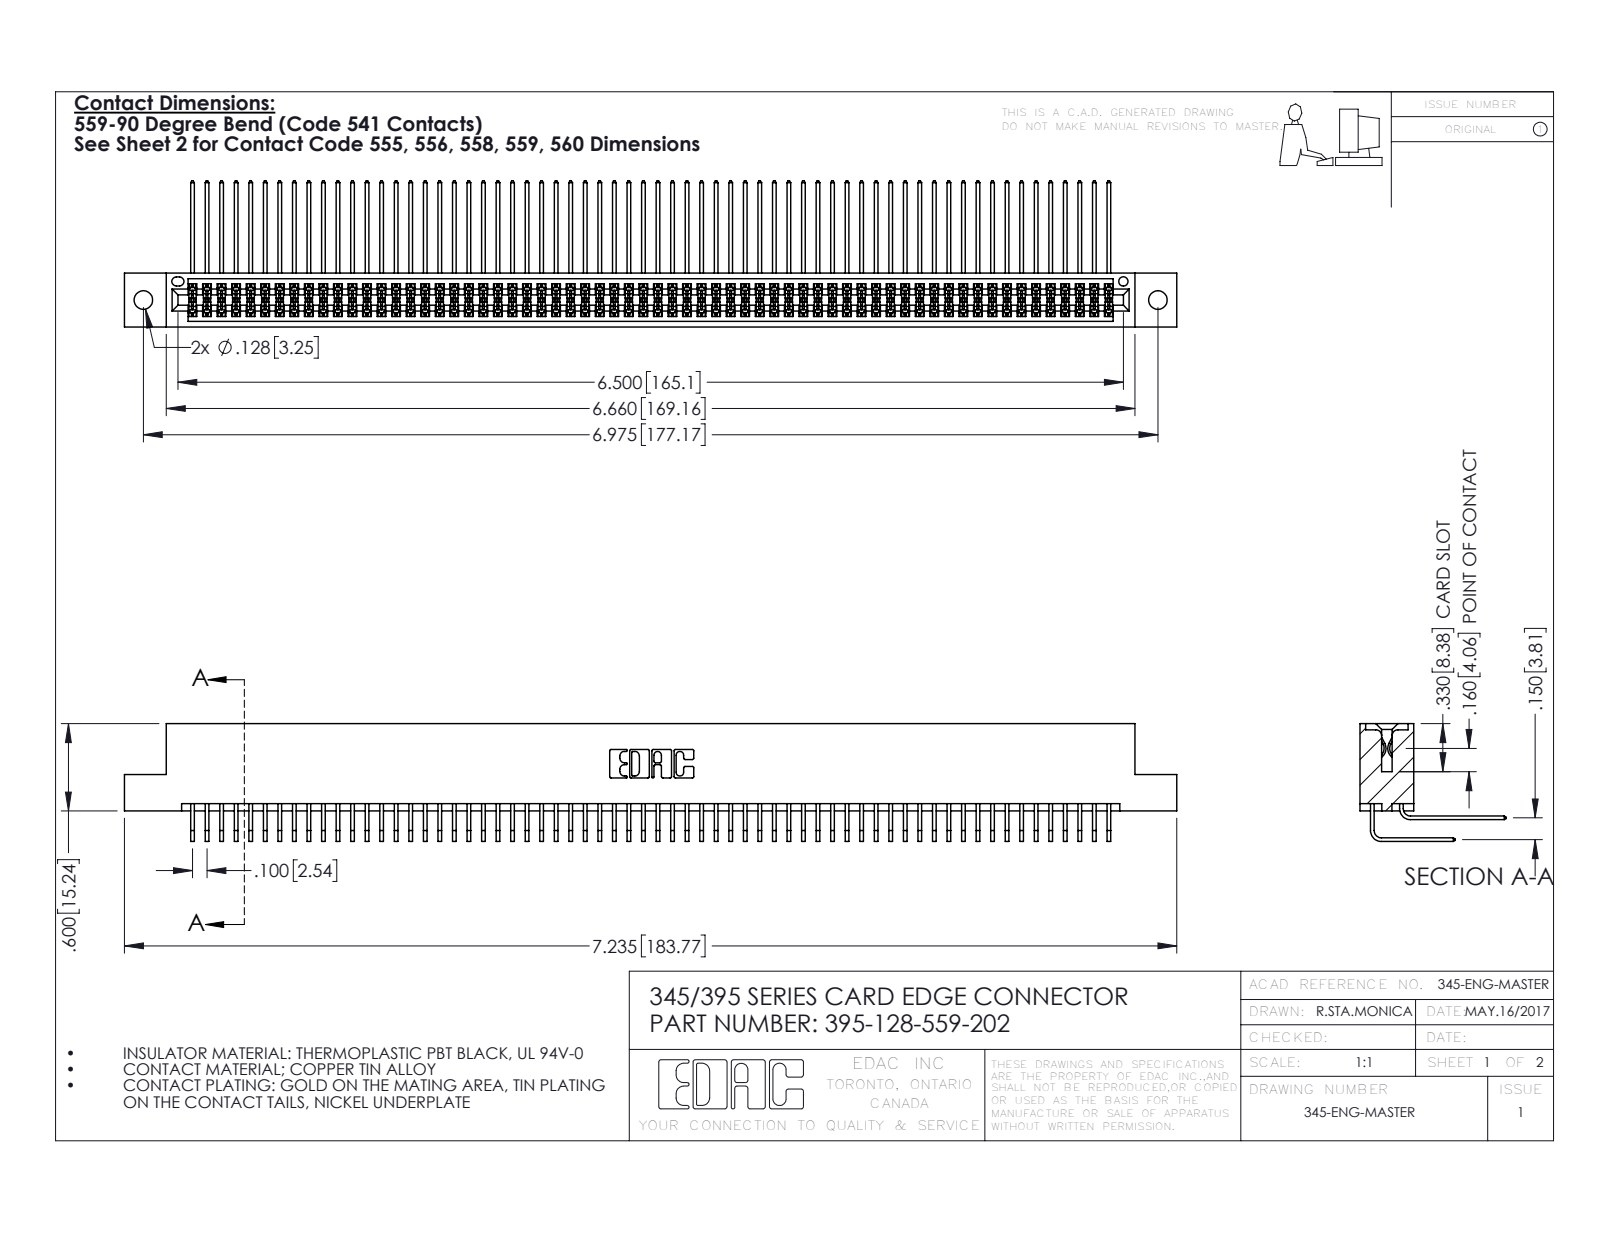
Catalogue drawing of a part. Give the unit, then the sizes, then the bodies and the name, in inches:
Units: inches
Overall size (bounding box): 7.235 × 1.005 × 0.809
Round holes (diameter × count): ⌀0.128 ×2, ⌀0.064 ×1
Partial cylindrical surfaces — rounded edges, fillets, slot ends (radius × count): R0.006 ×193, R0.01 ×22, R0.007 ×6, R0.031 ×6, R0.026 ×3, R0.014 ×2, R0.019 ×2, R0.022 ×2
Main face-to-face distances: 0.072, 0.298, 0.2, 0.37, 0.098, 0.272, 0.025, 0.225, 0.175, 0.15
Hole centre spacings: 0.27, 6.739, 6.975
Volume: 1.145 in³ · Surface area: 48.6 in²
Bodies: 129 solids, 6782 faces (4560 planar, 2222 cylindrical, 0 other)
Part name (STEP PRODUCT): 345-292-001_559 Tail - 2; 345 Part_Flush Mounting Lugs - 0.128 Dia; 345-292-001_558 559 Tail - 1; 395-128-559-202
STEP written by: SolidWorks 2016 (CONFIG_CONTROL_DESIGN)
